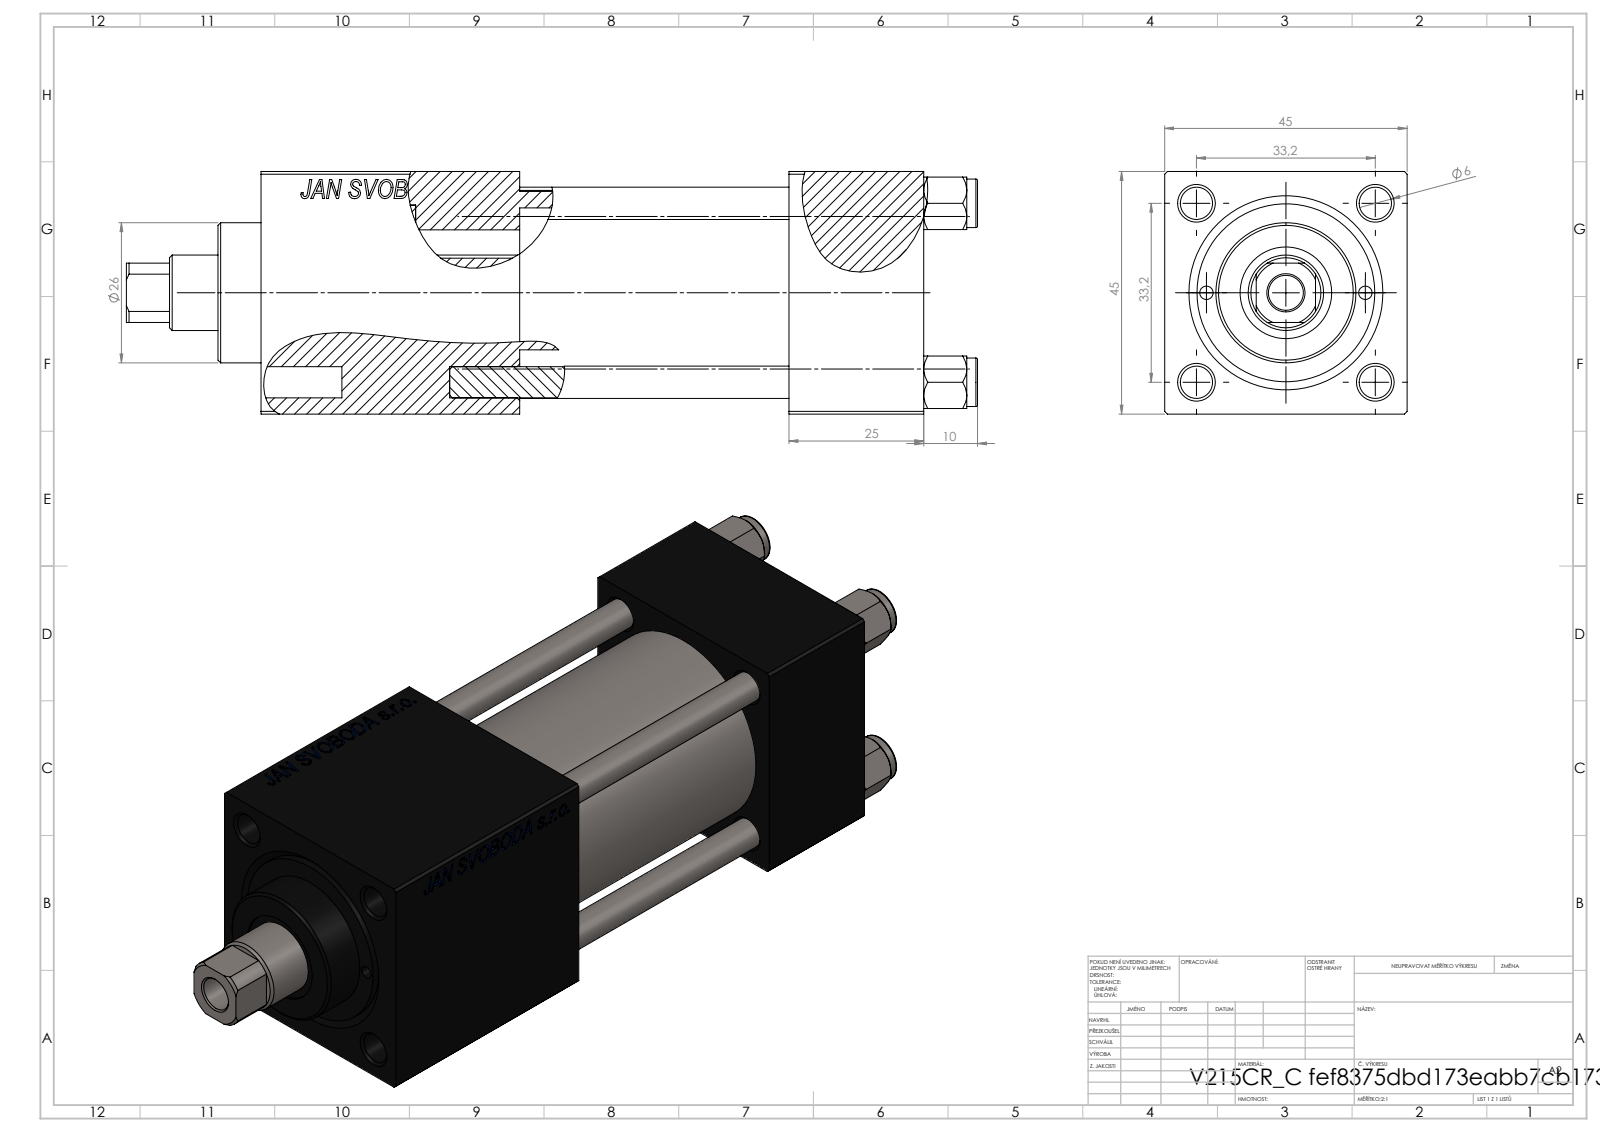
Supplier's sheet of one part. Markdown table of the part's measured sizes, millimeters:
| quantity | value |
| --- | --- |
| part name | V215_VC_A; V215CR_C_Body; NUT_M5_C; V215CR_VCP_C (+1 more) |
| STEP written by | SolidWorks 2019 (CONFIG_CONTROL_DESIGN) |
| units | millimeters |
| bodies | 11 solids, 1153 faces (527 planar, 90 cylindrical, 536 other) |
| overall size | 158 × 45 × 45 |
| volume | 193 847 mm³ |
| surface area | 67 163 mm² |
| round holes (diameter × count) | 6 × 4, 2.5 × 2, 7 × 2, 13.16 × 2, 20 × 2, 6.5 × 1, 14 × 1, 17 × 1, 24 × 1, 32 × 1, 33 × 1 |
| round bosses / shafts (diameter × count) | 9 × 4, 38 × 1, 26 × 1 |
| partial cylindrical surfaces (radius × count) | 6.5 × 1 |
| main face-to-face distances | 45, 25, 98, 123, 50, 75, 48, 94.3, 69.3, 19.3 |
| hole center spacings | 16.7, 23.48, 33.2, 35.47, 14.75, 46.95, 29.5, 75.5 |
